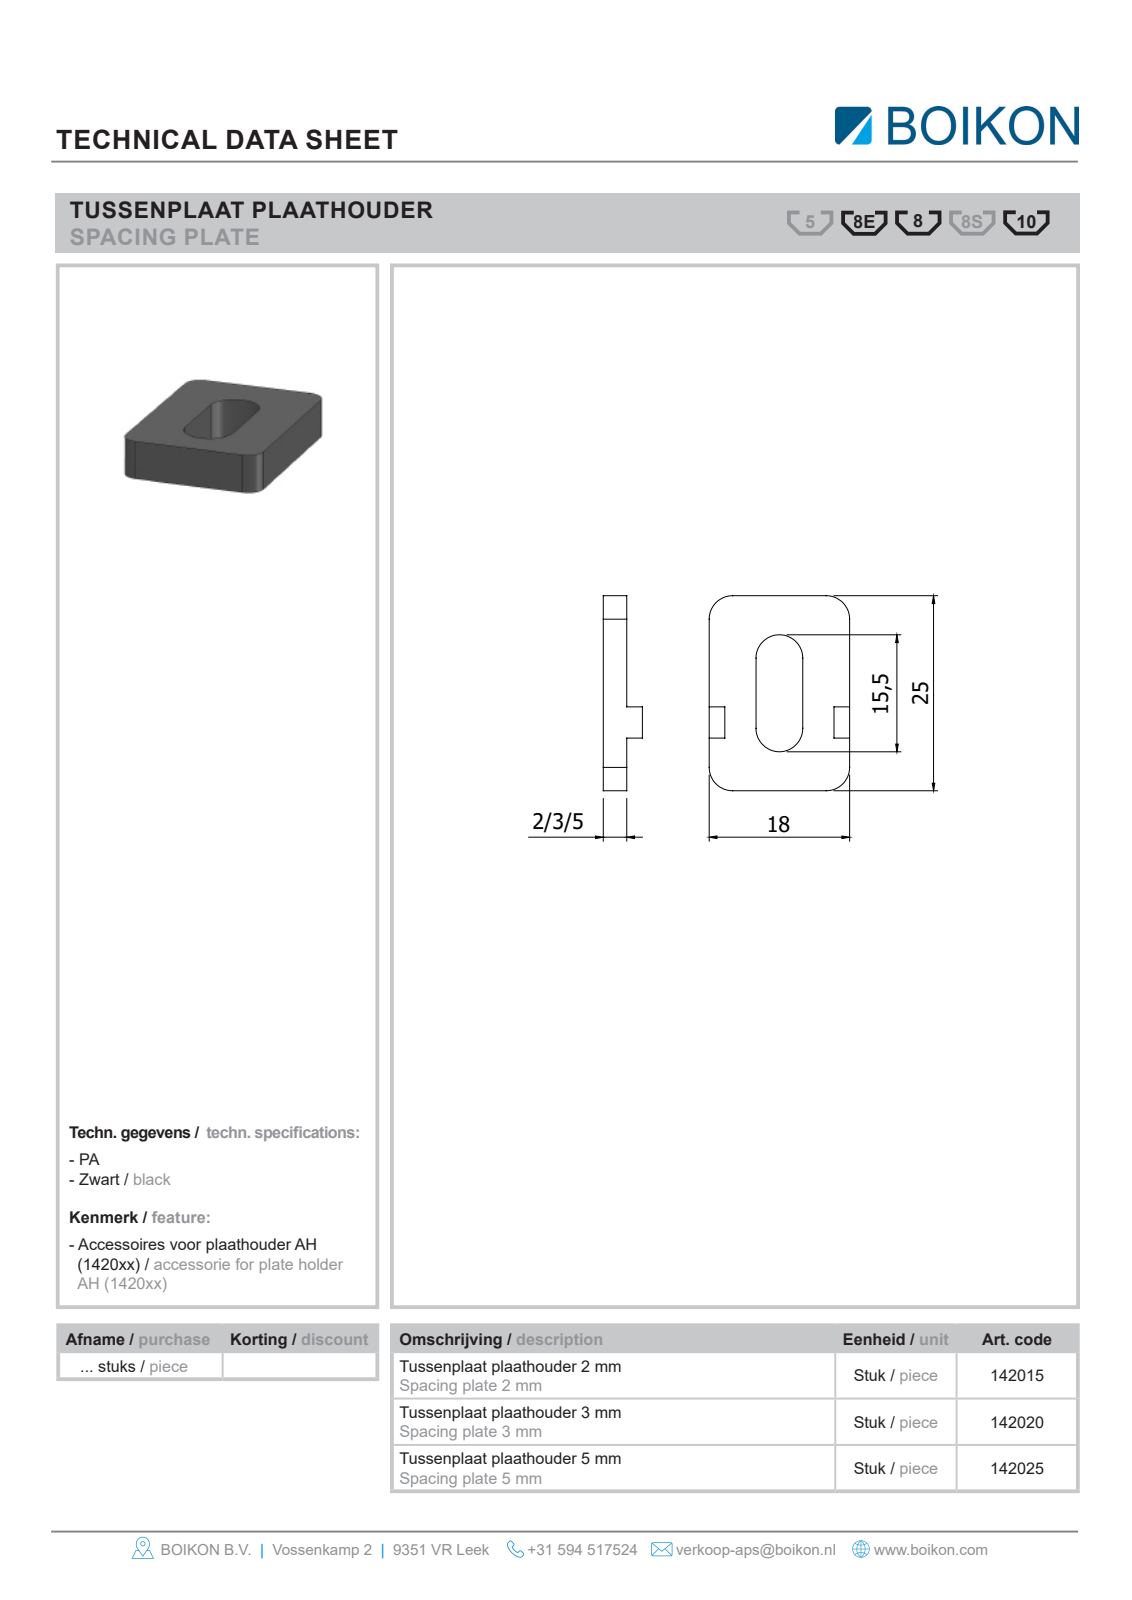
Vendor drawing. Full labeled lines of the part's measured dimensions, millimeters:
Part name (STEP PRODUCT): Root; 142015Tussenplaat plaathouder 2mmBOIKON
STEP written by: HiCAD 2013 1802.4 Build 509 (AUTOMOTIVE_DESIGN)
Units: millimetres
Bodies: 1 solid, 10 faces (8 planar, 2 cylindrical, 0 other)
Overall size (bounding box): 25 × 18.5 × 2
Volume: 742 mm³ · Surface area: 992 mm²
Partial cylindrical surfaces — rounded edges, fillets, slot ends (radius × count): R3.25 ×2
Main face-to-face distances: 2, 18.5, 25, 6, 12.5, 6.5
